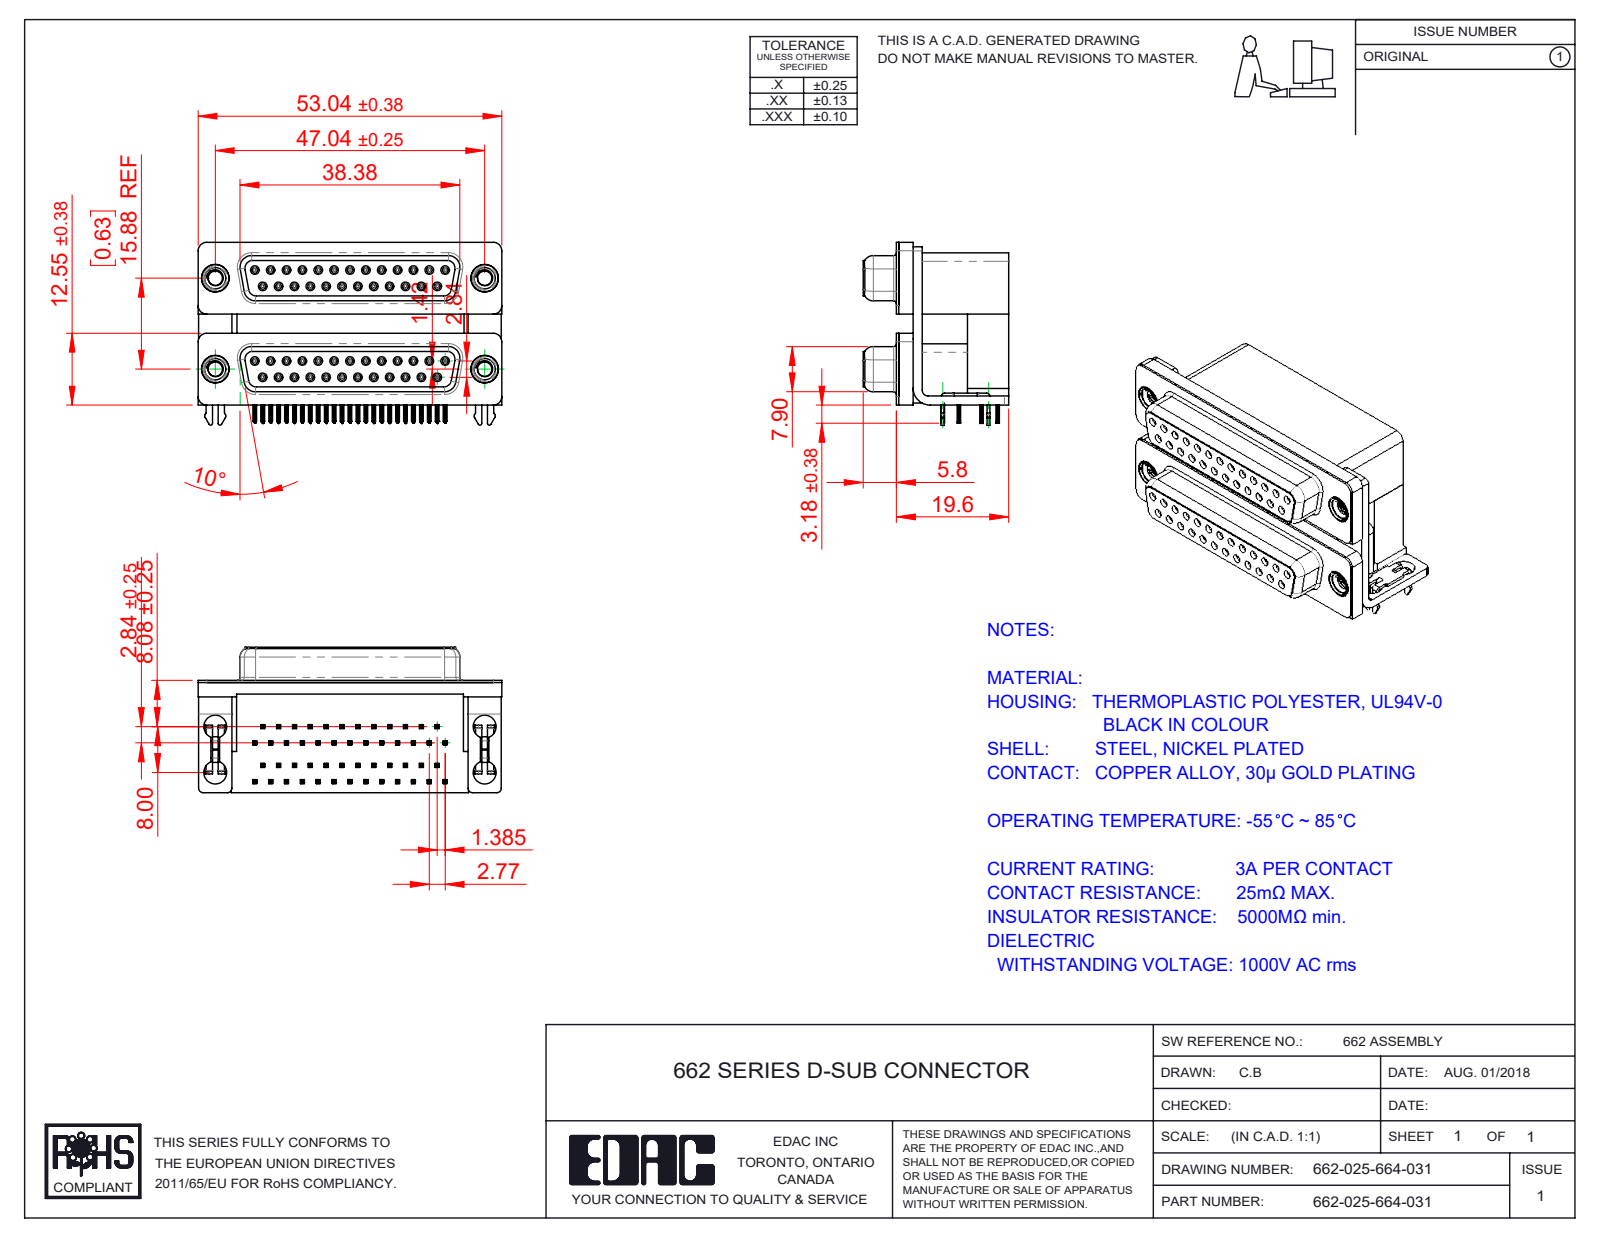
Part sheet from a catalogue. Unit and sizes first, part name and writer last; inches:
Units: inches
Overall size (bounding box): 2.088 × 1.257 × 1
Round holes (diameter × count): ⌀0.031 ×50, ⌀0.035 ×50, ⌀0.157 ×8, ⌀0.098 ×4, ⌀0.138 ×4, ⌀0.189 ×4, ⌀0.197 ×4
Round bosses / shafts (diameter × count): ⌀0.047 ×50, ⌀0.193 ×4, ⌀0.187 ×4, ⌀0.154 ×4
Partial cylindrical surfaces — rounded edges, fillets, slot ends (radius × count): R0.004 ×402, R0.006 ×200, R0.014 ×100, R0.013 ×50, R0.011 ×24, R0.053 ×18, R0.059 ×13, R0.02 ×12
Main face-to-face distances: 0.625, 0.756, 0.016, 0.283, 0.472, 0.421, 0.244, 0.657, 0.374, 0.098
Hole centre spacings: 0.124, 0.109, 0.218, 0.436, 0.327, 0.198, 0.545, 0.294
Volume: 1.397 in³ · Surface area: 39.12 in²
Bodies: 63 solids, 7948 faces (3678 planar, 1862 cylindrical, 2408 other)
Part name (STEP PRODUCT): 662 Shell_25 Contacts; 662 Contact Top Lower; 662 Housing Upper_25 Contacts L; 662-025-664-031 (+8 more)
STEP written by: SolidWorks 2020 (CONFIG_CONTROL_DESIGN)
